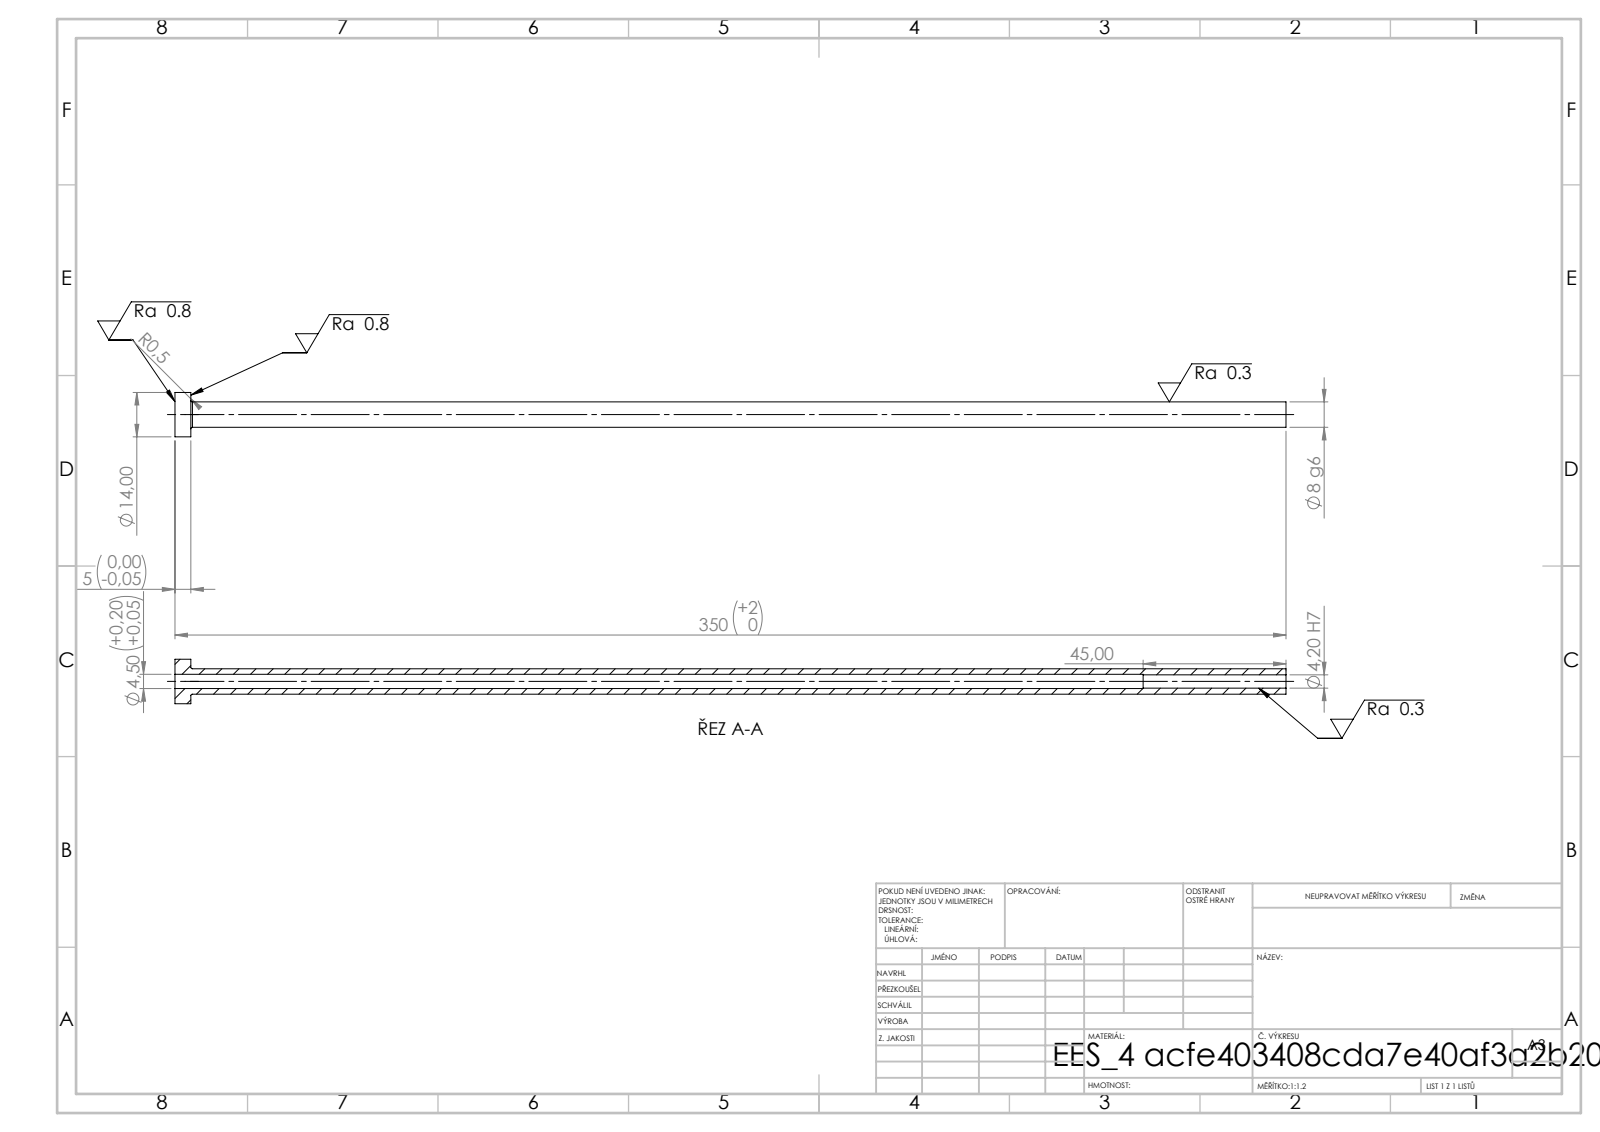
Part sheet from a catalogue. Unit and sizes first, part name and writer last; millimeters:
Units: millimetres
Overall size (bounding box): 350 × 14 × 14
Round holes (diameter × count): ⌀4.2 ×1, ⌀4.5 ×1
Round bosses / shafts (diameter × count): ⌀14 ×1, ⌀8 ×1
Main face-to-face distances: 5, 350, 345, 305, 300, 45
Volume: 12 638 mm³ · Surface area: 14 071 mm²
Bodies: 1 solid, 14 faces (4 planar, 8 cylindrical, 2 other)
STEP written by: SolidWorks 2019 (CONFIG_CONTROL_DESIGN)
